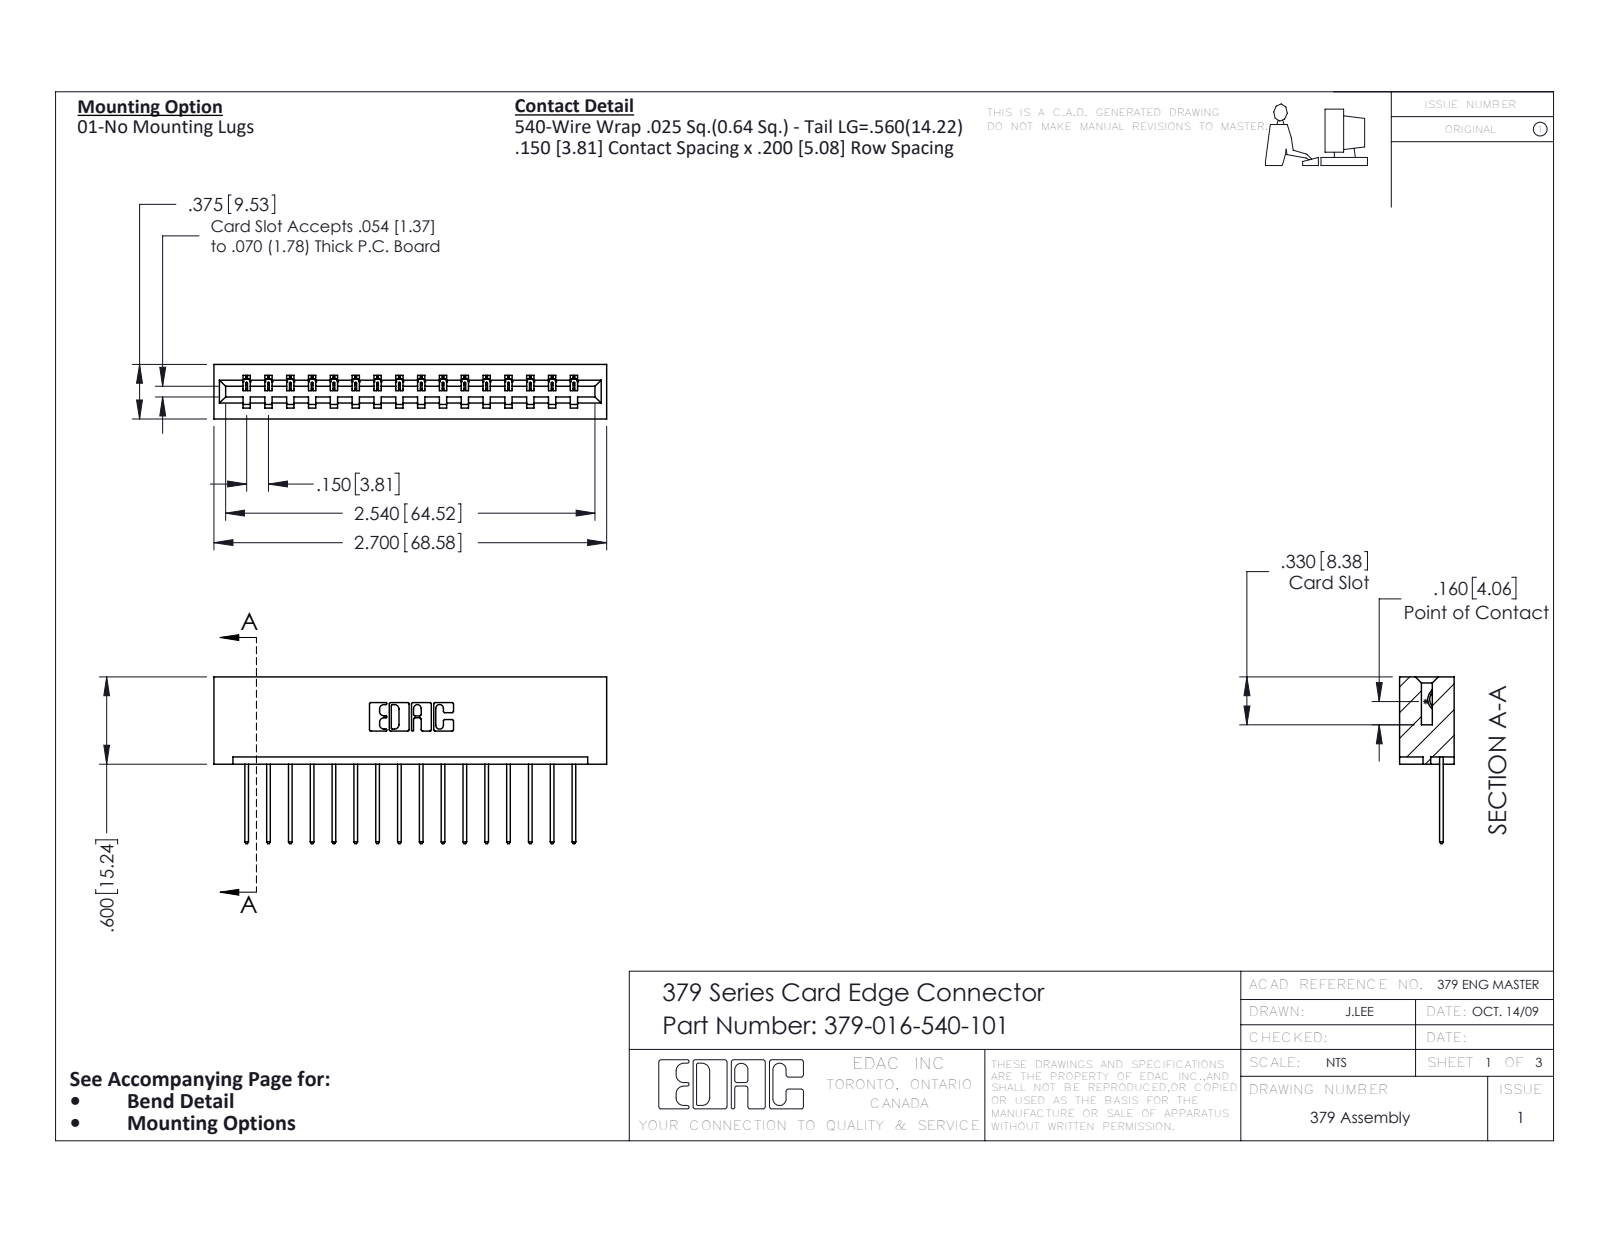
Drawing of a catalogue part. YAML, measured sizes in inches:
part_name: "345-292-001_345-293-140; 379 Part_Lugless; 379-016-540-101"
step_written_by: "SolidWorks 2020 (CONFIG_CONTROL_DESIGN)"
units: inches
bodies: {solids: 17, faces: 1034, planar: 738, cylindrical: 296, other: 0}
overall_size: [2.7, 1.147, 0.375]
volume: 0.466
surface_area: 12.11
partial_cylinders:
  - {radius: 0.006, count: 32}
  - {radius: 0.01, count: 32}
  - {radius: 0.01, count: 22}
  - {radius: 0.007, count: 6}
  - {radius: 0.031, count: 6}
  - {radius: 0.026, count: 3}
  - {radius: 0.014, count: 1}
  - {radius: 0.022, count: 1}
face_to_face_distances: [0.3, 0.075, 0.375, 0.15, 0.6, 0.225, 0.2, 0.45, 0.1, 0.75]
